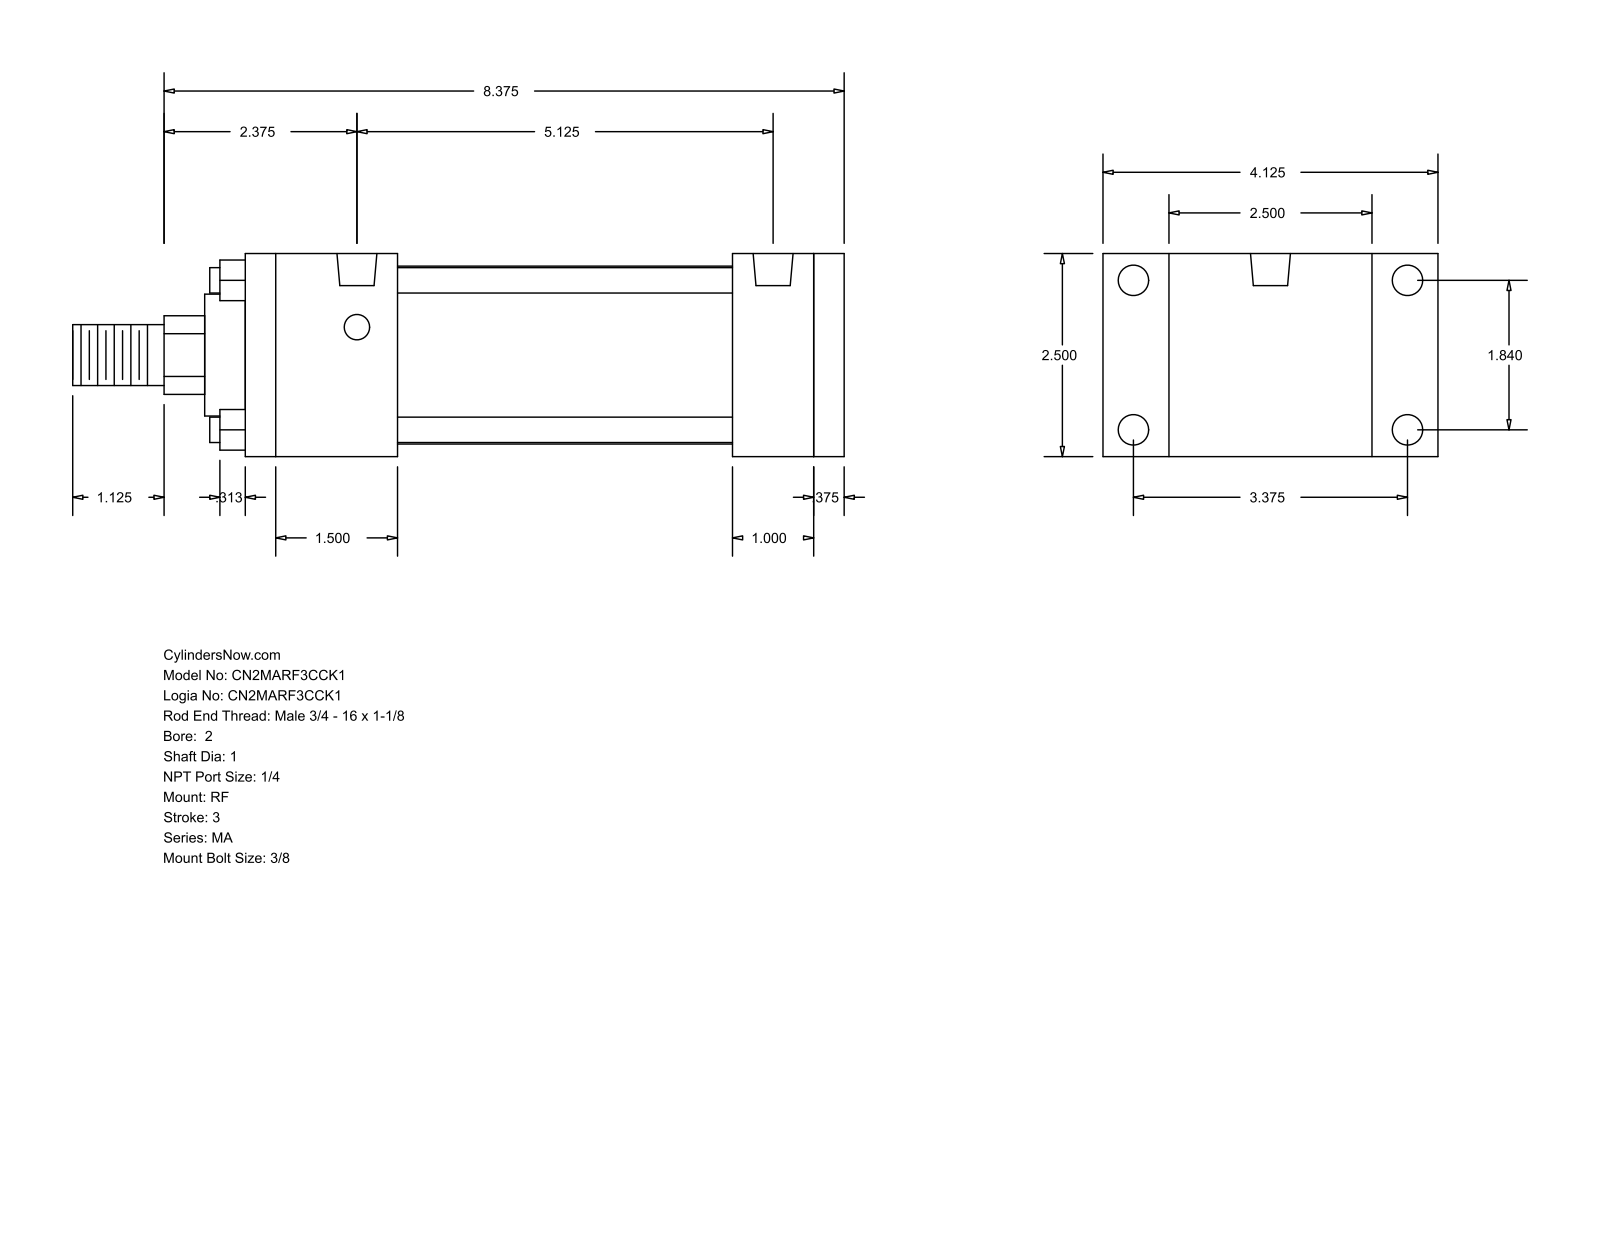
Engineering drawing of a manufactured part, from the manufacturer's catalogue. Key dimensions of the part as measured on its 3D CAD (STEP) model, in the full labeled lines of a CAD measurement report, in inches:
Part name (STEP PRODUCT): MA_RF__0200_1
STEP written by: GSSL Pune (CONFIG_CONTROL_DESIGN)
Units: inches
Bodies: 0 solids, 92 faces (64 planar, 28 cylindrical, 0 other)
Overall size (bounding box): 9.5 × 4.125 × 2.5
Round holes (diameter × count): ⌀0.313 ×4, ⌀0.375 ×4, ⌀0.492 ×2
Round bosses / shafts (diameter × count): ⌀0.313 ×4, ⌀2.19 ×1, ⌀1.5 ×1, ⌀1 ×1, ⌀0.75 ×1
Partial cylindrical surfaces — rounded edges, fillets, slot ends (radius × count): R0.484 ×1
Main face-to-face distances: 2.5, 7, 0.375, 7.375, 1, 0.813, 0.5, 1.875, 5.125, 5.5
Hole centre spacings: 1.84, 3.375, 3.844, 5.125
